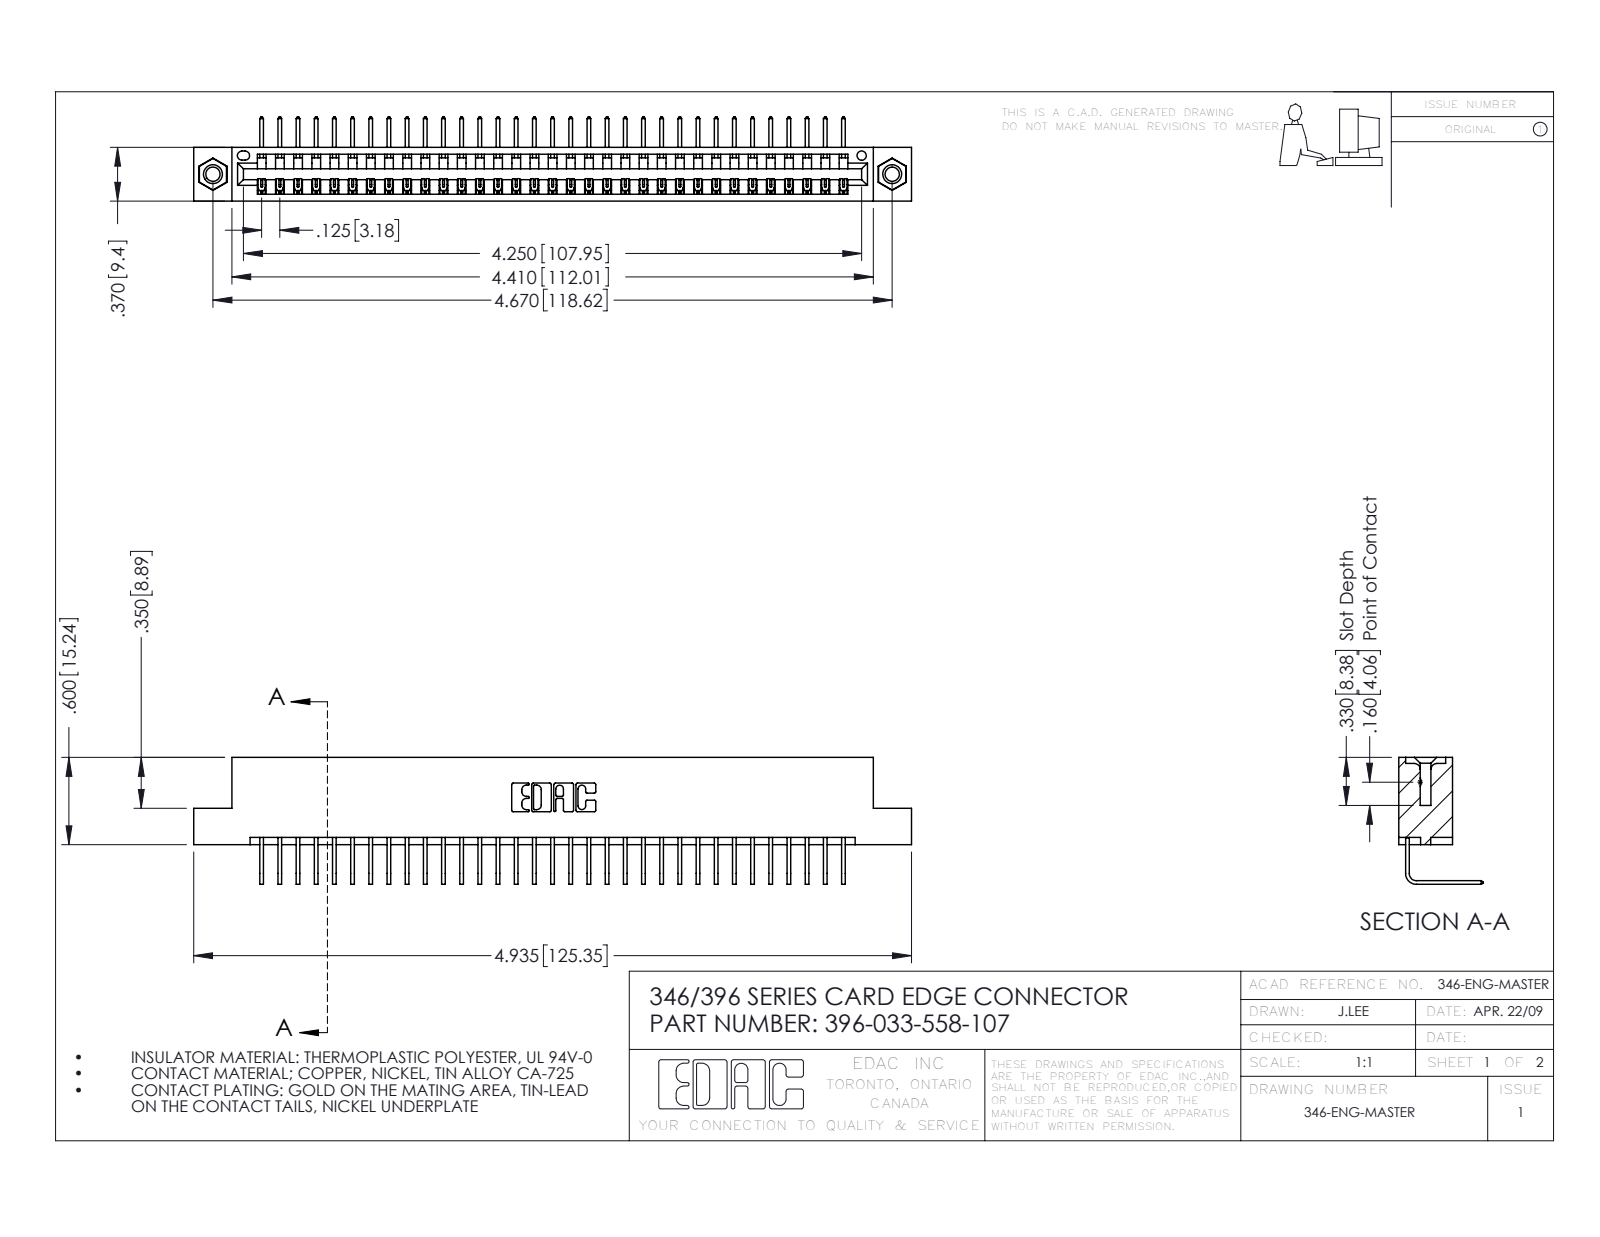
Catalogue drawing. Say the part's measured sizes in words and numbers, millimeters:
The part is named "345-250-001_345-250-005-103; 346 Part_Flush Mounting Lugs - 0.156 Dia-TI; 345-292-001_558 Tail - 2; 396-033-558-107". Its 3-D file was written by "SolidWorks 2016 (CONFIG_CONTROL_DESIGN)". It is 36 solids with 2162 faces: 1494 planar, 652 cylindrical and 16 other. Overall it measures 125.3 by 22.2 by 14.7 millimeters. Its volume is 12 000 cubic millimeters and its surface area 15 630 square millimeters. Round holes: 2 of diameter 2.5, 2 of diameter 3.2, 2 of diameter 4, 1 of diameter 1.6. Round bosses or shafts: 2 of diameter 3.9. Partial cylindrical surfaces (rounded edges, fillets, slot ends): 66 of radius 0.2, 22 of radius 0.3, 6 of radius 0.2, 6 of radius 0.8, 3 of radius 0.7, 2 of radius 0.8, 2 of radius 1, 1 of radius 0.4. The main face-to-face distances are 8.2, 1.2, 9.4, 6.4, 7.6, 0.6, 1.8, 3.8, 5.6, 2.5. The hole center spacings are 6.2, 113.3, 118.6.
